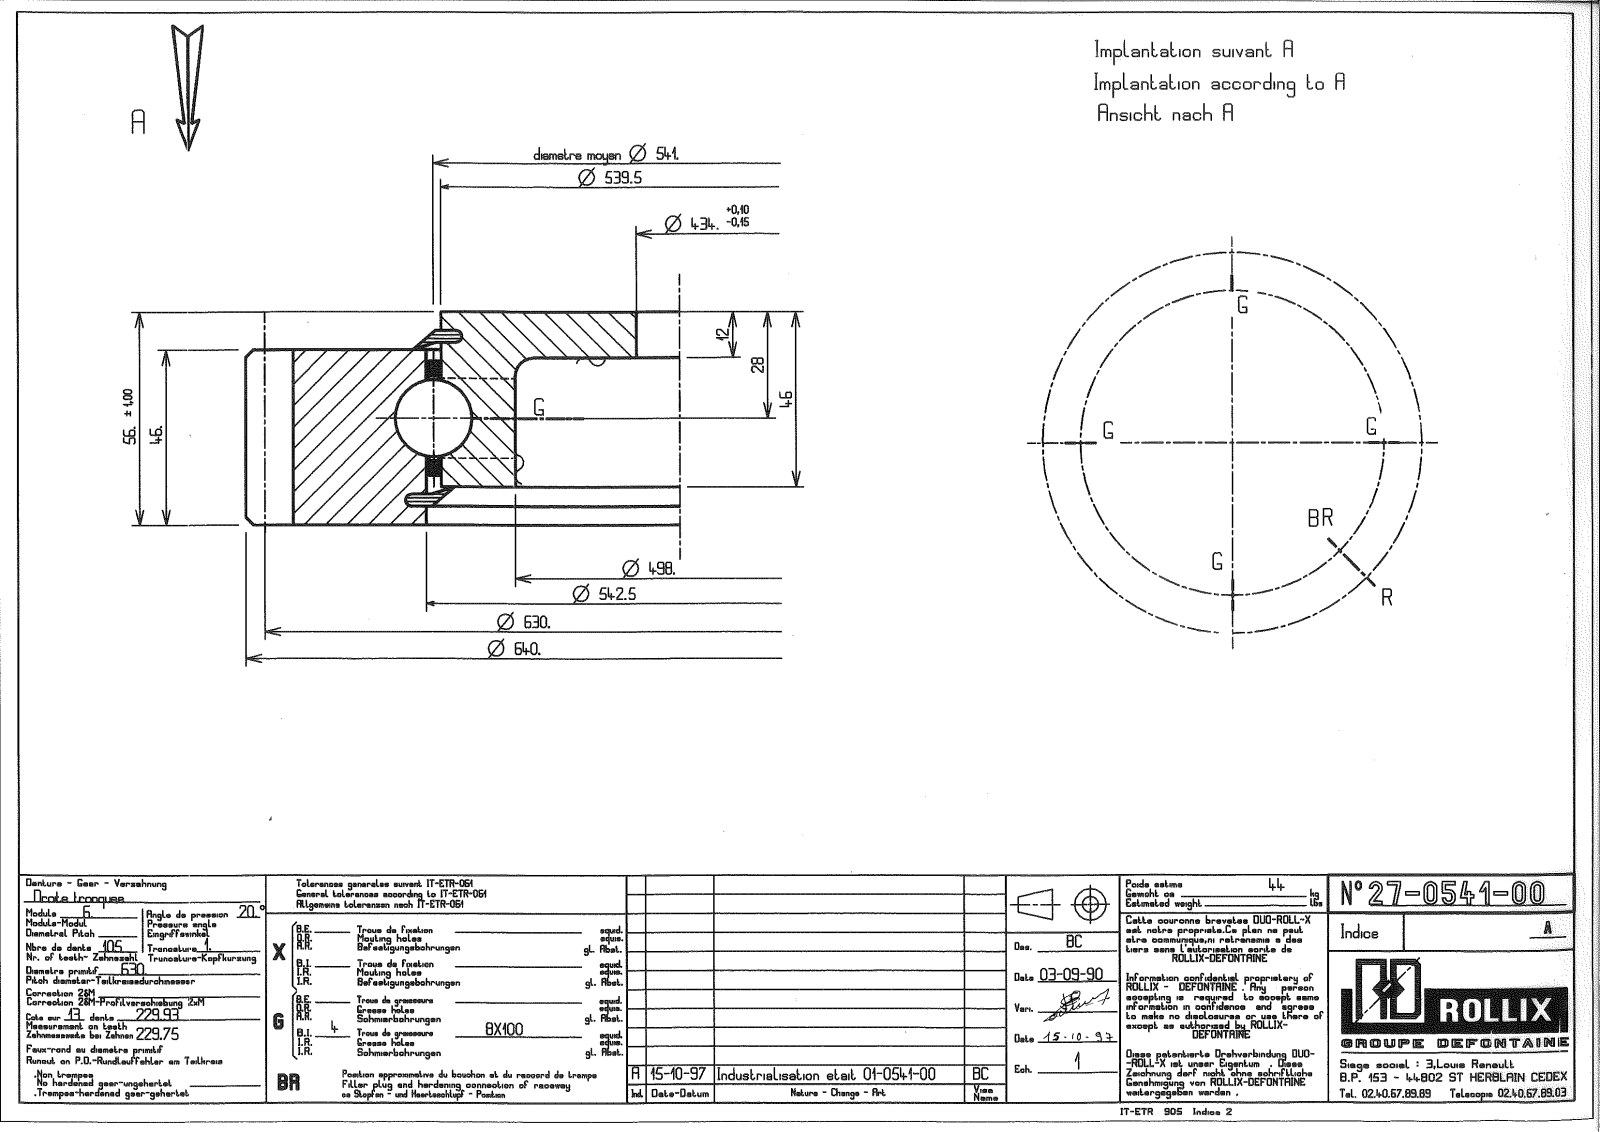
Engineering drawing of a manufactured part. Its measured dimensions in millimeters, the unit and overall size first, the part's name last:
Units: millimetres
Overall size (bounding box): 639.99 × 639.93 × 56
Round holes (diameter × count): ⌀7 ×4, ⌀434 ×1, ⌀498 ×1, ⌀545.5 ×1
Round bosses / shafts (diameter × count): ⌀8 ×4, ⌀536.5 ×1
Partial cylindrical surfaces — rounded edges, fillets, slot ends (radius × count): R307.5 ×1, R320 ×1
Main face-to-face distances: 10, 46, 56, 44, 2, 12, 34, 36, 8.05, 47.95
Volume: 5 237 000 mm³ · Surface area: 865 946 mm²
Bodies: 9 solids, 787 faces (263 planar, 243 cylindrical, 281 other)
Part name (STEP PRODUCT): 21-0541-00
STEP written by: SolidWorks 2016 (CONFIG_CONTROL_DESIGN)
